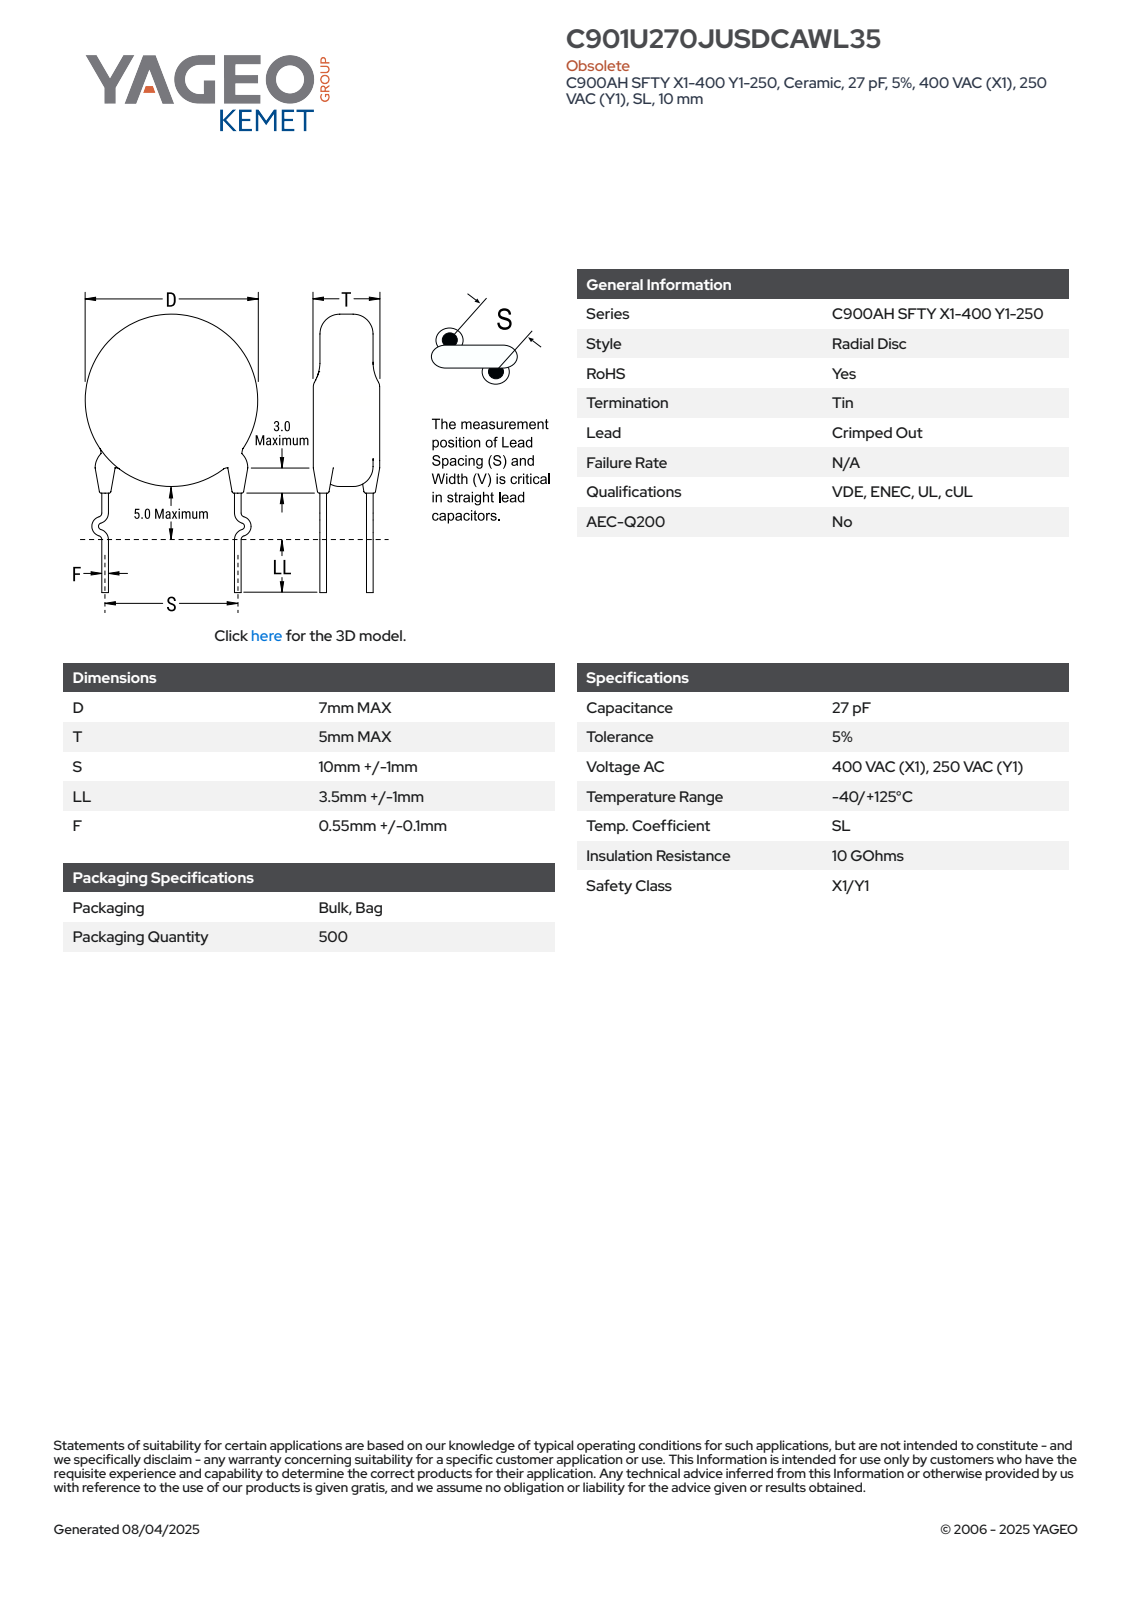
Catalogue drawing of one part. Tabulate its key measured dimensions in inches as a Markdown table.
| quantity | value |
| --- | --- |
| part name | CCD_KCOC900_D7T5S10LL4.5F0.55 |
| STEP written by | SolidWorks 2014 (AUTOMOTIVE_DESIGN) |
| units | inches |
| bodies | 4 solids, 93 faces (63 planar, 10 cylindrical, 20 other) |
| overall size | 0.65 × 0.547 × 0.27 |
| volume | 0.012 in³ |
| surface area | 0.377 in² |
| round bosses / shafts (diameter × count) | 0.047 × 4, 0.276 × 1 |
| main face-to-face distances | 0.197, 0.029, 0.152, 0.124, 0.023, 0.013, 0.117, 0.059, 0.085, 0.088 |
